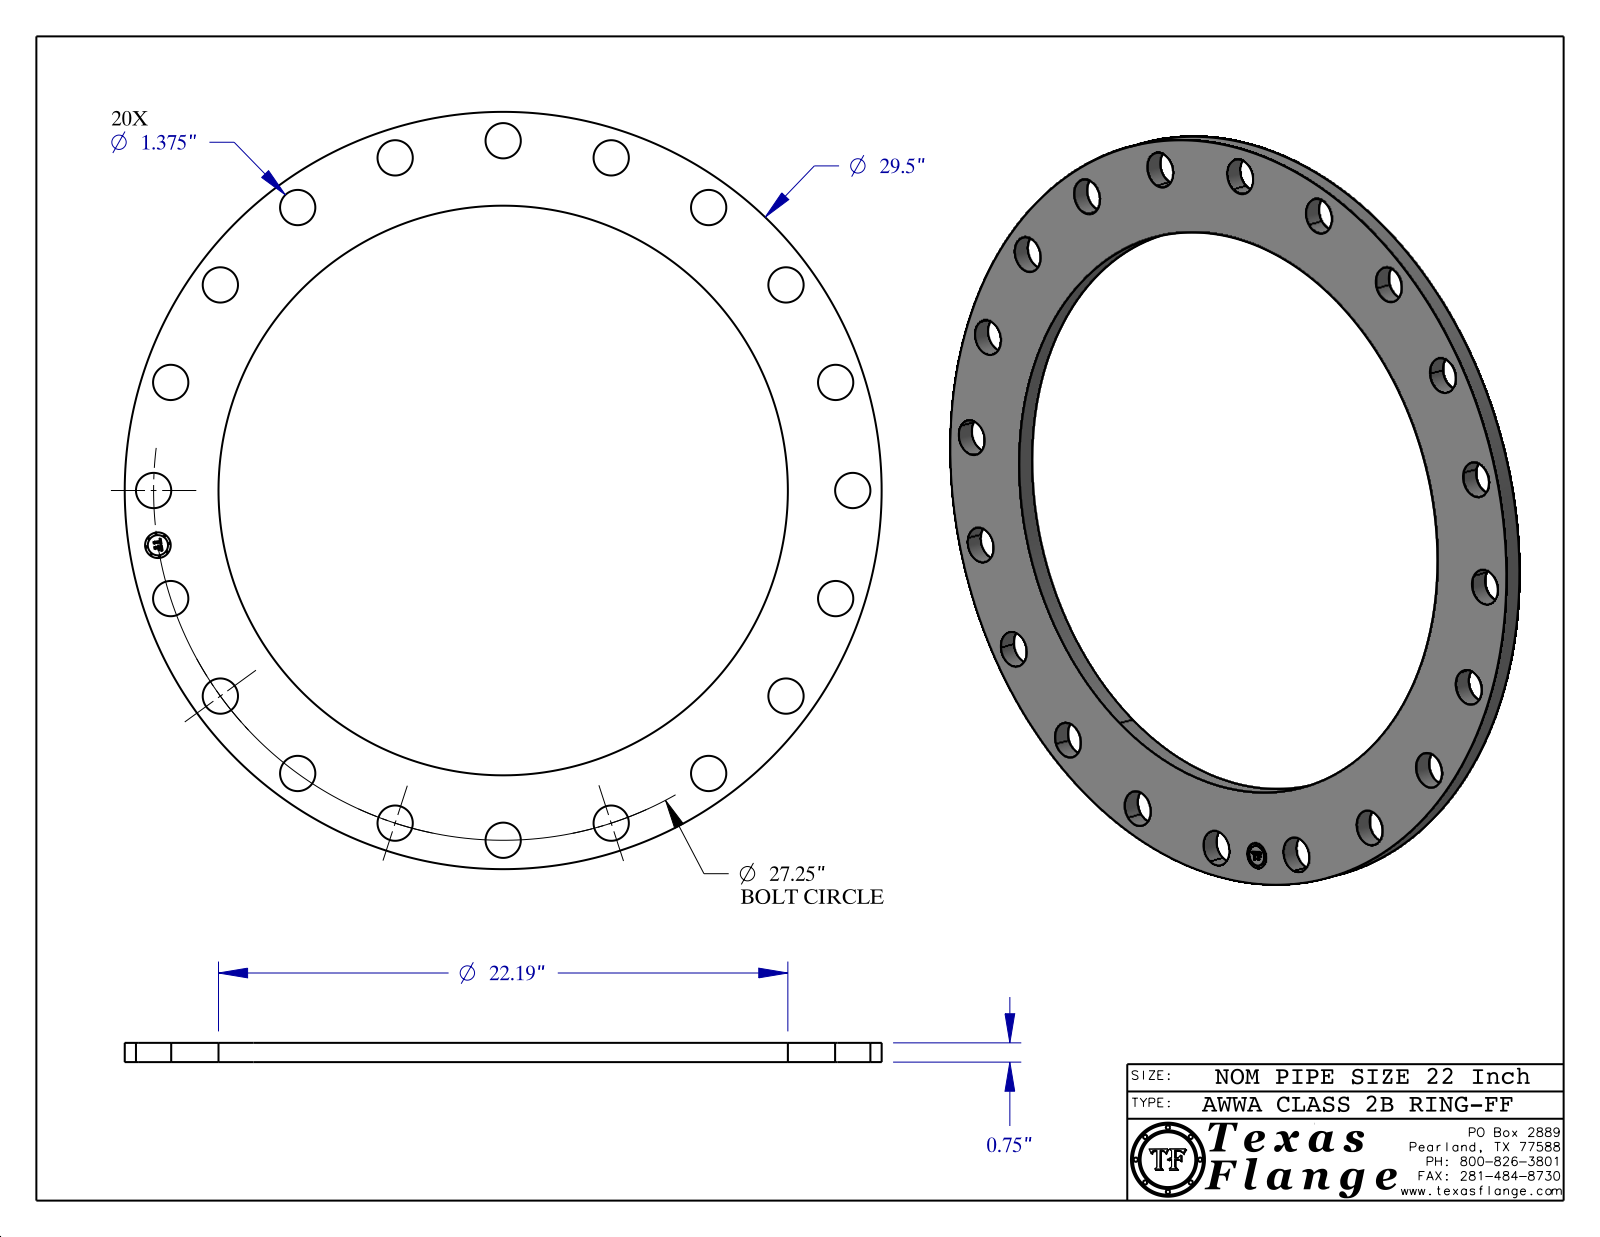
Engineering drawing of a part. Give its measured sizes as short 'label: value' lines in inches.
name: AWWA Class 2B-RING-FF
written by: CATIA V5 STEP AP214 (AUTOMOTIVE_DESIGN)
unit: in
bodies: 1 solid, 431 faces (367 planar, 64 cylindrical, 0 other)
size: 29.5 × 29.5 × 0.75
volume: 200.3 in³; area: 720.9 in²
holes: 20× ⌀1.375, 1× ⌀1, 1× ⌀22.19
bosses: 8× ⌀0.061, 1× ⌀29.5, 1× ⌀0.788
face distances: 0.75, 0.735, 0.015, 0.298, 0.293, 0.054, 0.193, 0.248, 0.044, 0.15
hole spacings: 13.625, 19.269, 25.917, 8.421, 12.371, 4.263, 16.017, 22.046
